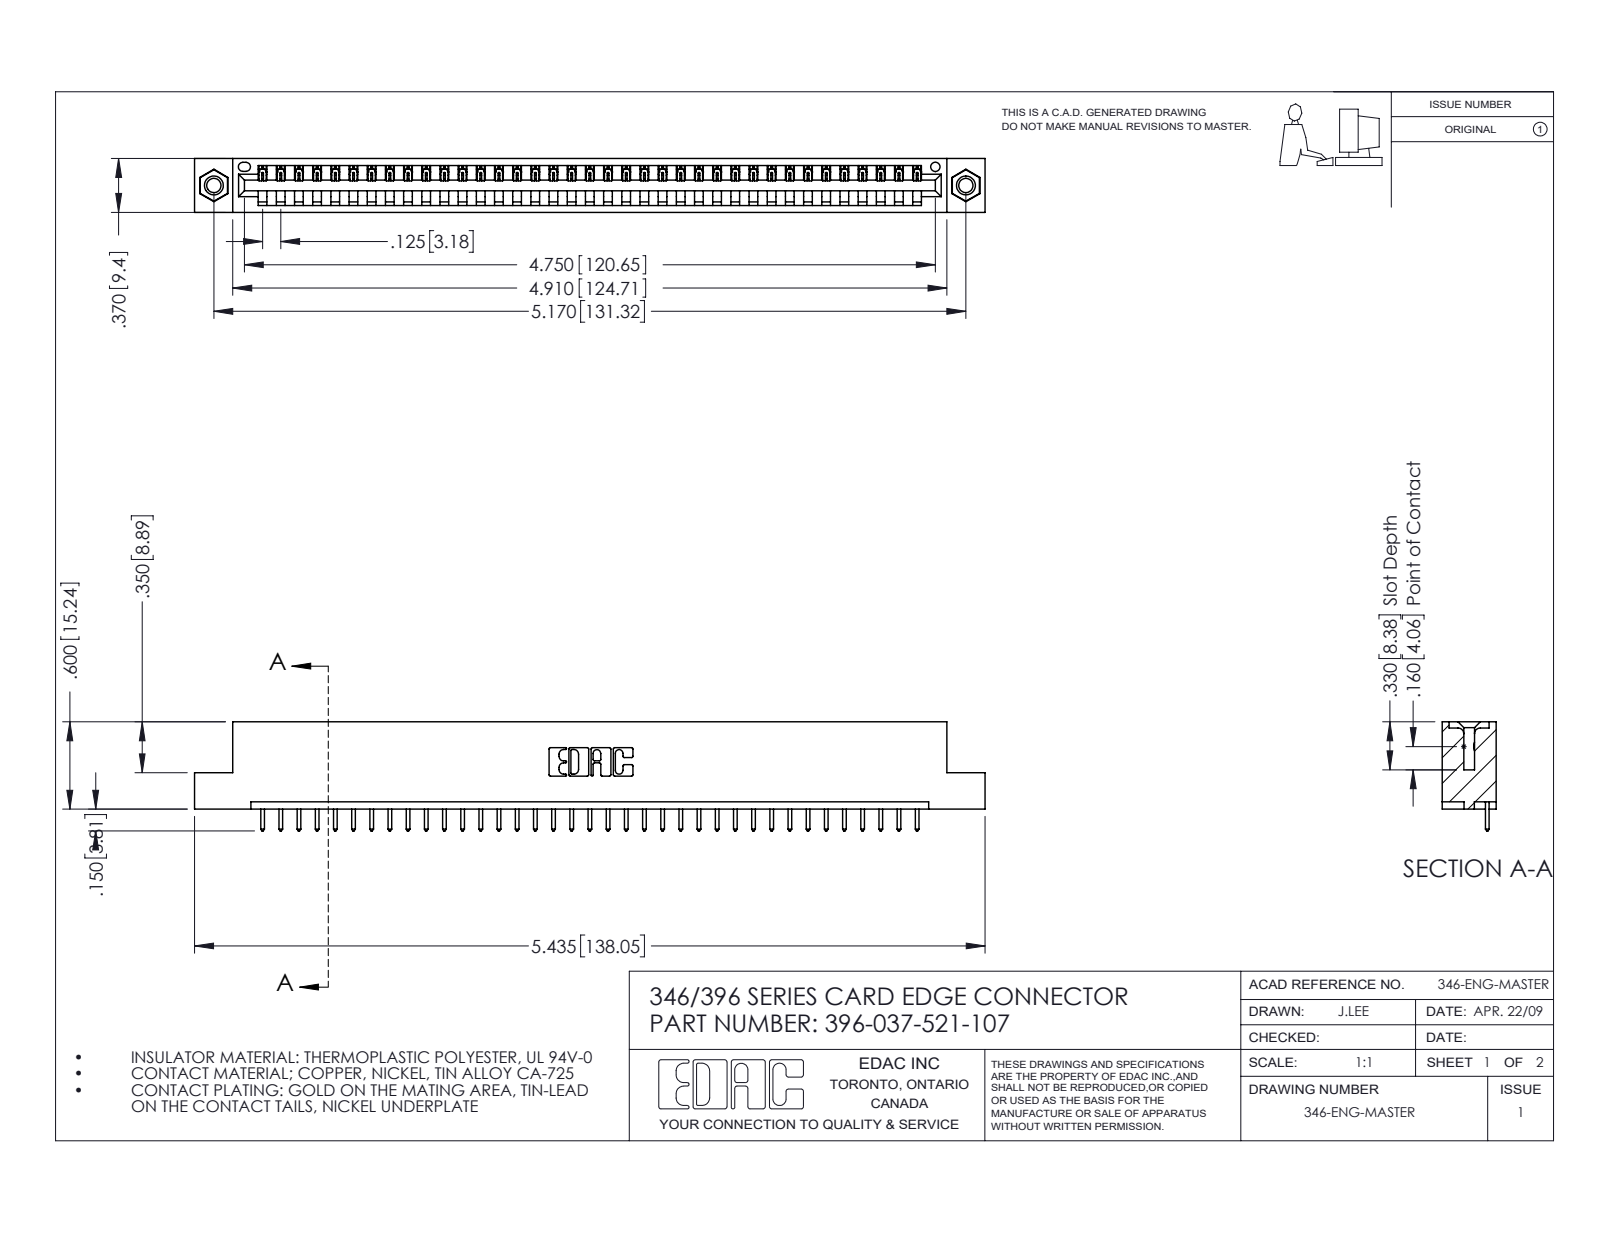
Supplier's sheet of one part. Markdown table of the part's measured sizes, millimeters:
| quantity | value |
| --- | --- |
| part name | 396-037-521-107; 346 Part_Flush Mounting Lugs - 0.156 Dia-TI; 345-250-001_345-250-005-103; 345-292-001_345-293-121 |
| STEP written by | SolidWorks 2016 (CONFIG_CONTROL_DESIGN) |
| units | millimeters |
| bodies | 40 solids, 2328 faces (1588 planar, 724 cylindrical, 16 other) |
| overall size | 138 × 19.1 × 9.4 |
| volume | 13 100 mm³ |
| surface area | 15 880 mm² |
| round holes (diameter × count) | 2.5 × 2, 3.2 × 2, 4 × 2, 1.6 × 1 |
| round bosses / shafts (diameter × count) | 3.9 × 2 |
| partial cylindrical surfaces (radius × count) | 0.2 × 74, 0.3 × 74, 0.3 × 22, 0.2 × 6, 0.8 × 6, 0.7 × 3, 0.8 × 2, 1 × 2 |
| main face-to-face distances | 1.2, 8.2, 9.4, 6.4, 1.8, 7.6, 0.6, 3.8, 5.6, 2.5 |
| hole center spacings | 6.2, 126, 131.3 |
